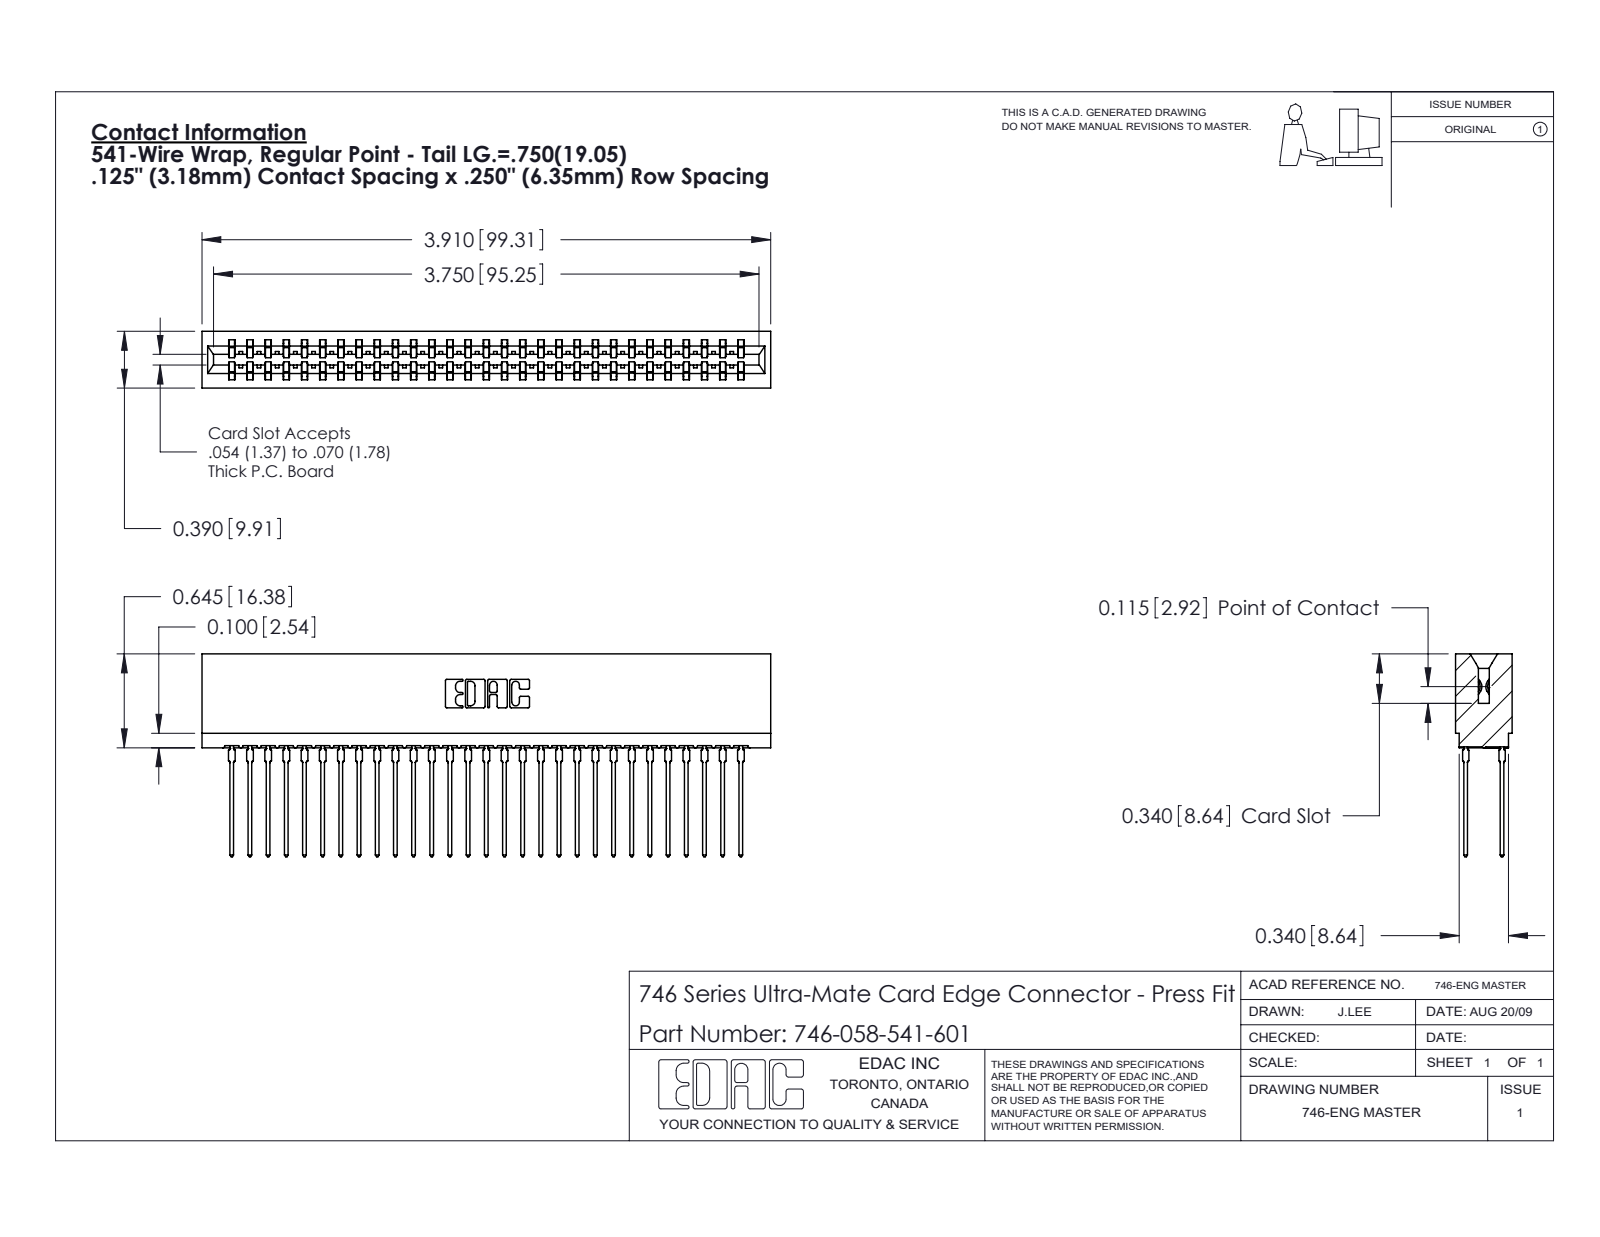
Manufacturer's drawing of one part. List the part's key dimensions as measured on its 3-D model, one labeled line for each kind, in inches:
Part name (STEP PRODUCT): 746-058-541-601; 746 Part_.340 Slot Depth - 01; 746-292-001_541
STEP written by: SolidWorks 2020 (CONFIG_CONTROL_DESIGN)
Units: inches
Bodies: 59 solids, 5288 faces (2723 planar, 1057 cylindrical, 1508 other)
Overall size (bounding box): 3.91 × 1.394 × 0.39
Volume: 0.721 in³ · Surface area: 28.84 in²
Partial cylindrical surfaces — rounded edges, fillets, slot ends (radius × count): R0.021 ×116, R0.015 ×30, R0.01 ×22, R0.005 ×8, R0.011 ×8, R0.007 ×6, R0.031 ×6, R0.026 ×3
Main face-to-face distances: 0.057, 0.333, 0.25, 0.025, 0.307, 0.39, 0.083, 0.275, 0.5, 0.042
